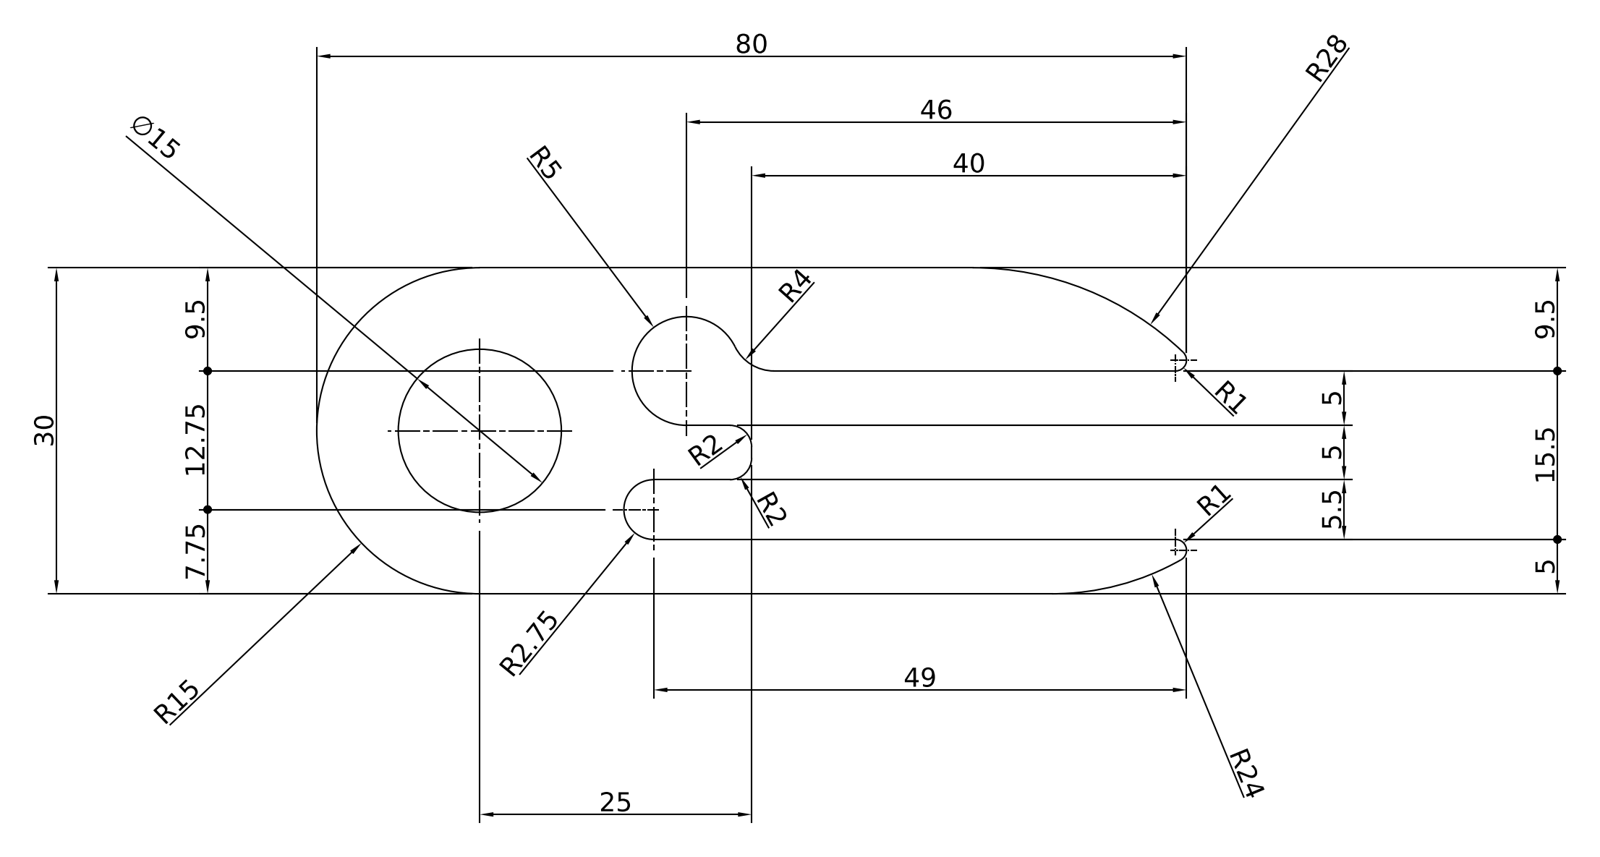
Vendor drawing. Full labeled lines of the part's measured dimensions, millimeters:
Part name (STEP PRODUCT): BPRCR0000029
STEP written by: Autodesk Inventor 2019 (AUTOMOTIVE_DESIGN)
Units: millimetres
Bodies: 1 solid, 20 faces (9 planar, 11 cylindrical, 0 other)
Overall size (bounding box): 1000 × 80 × 30
Volume: 1 290 000 mm³ · Surface area: 371 139 mm²
Round holes (diameter × count): ⌀15 ×1
Partial cylindrical surfaces — rounded edges, fillets, slot ends (radius × count): R1 ×2, R2 ×2, R2.75 ×1, R4 ×1, R5 ×1, R15 ×1, R24 ×1, R28 ×1
Main face-to-face distances: 5, 25, 30, 15.5, 9.5, 20.5, 10.5, 19.5, 10, 5.5
